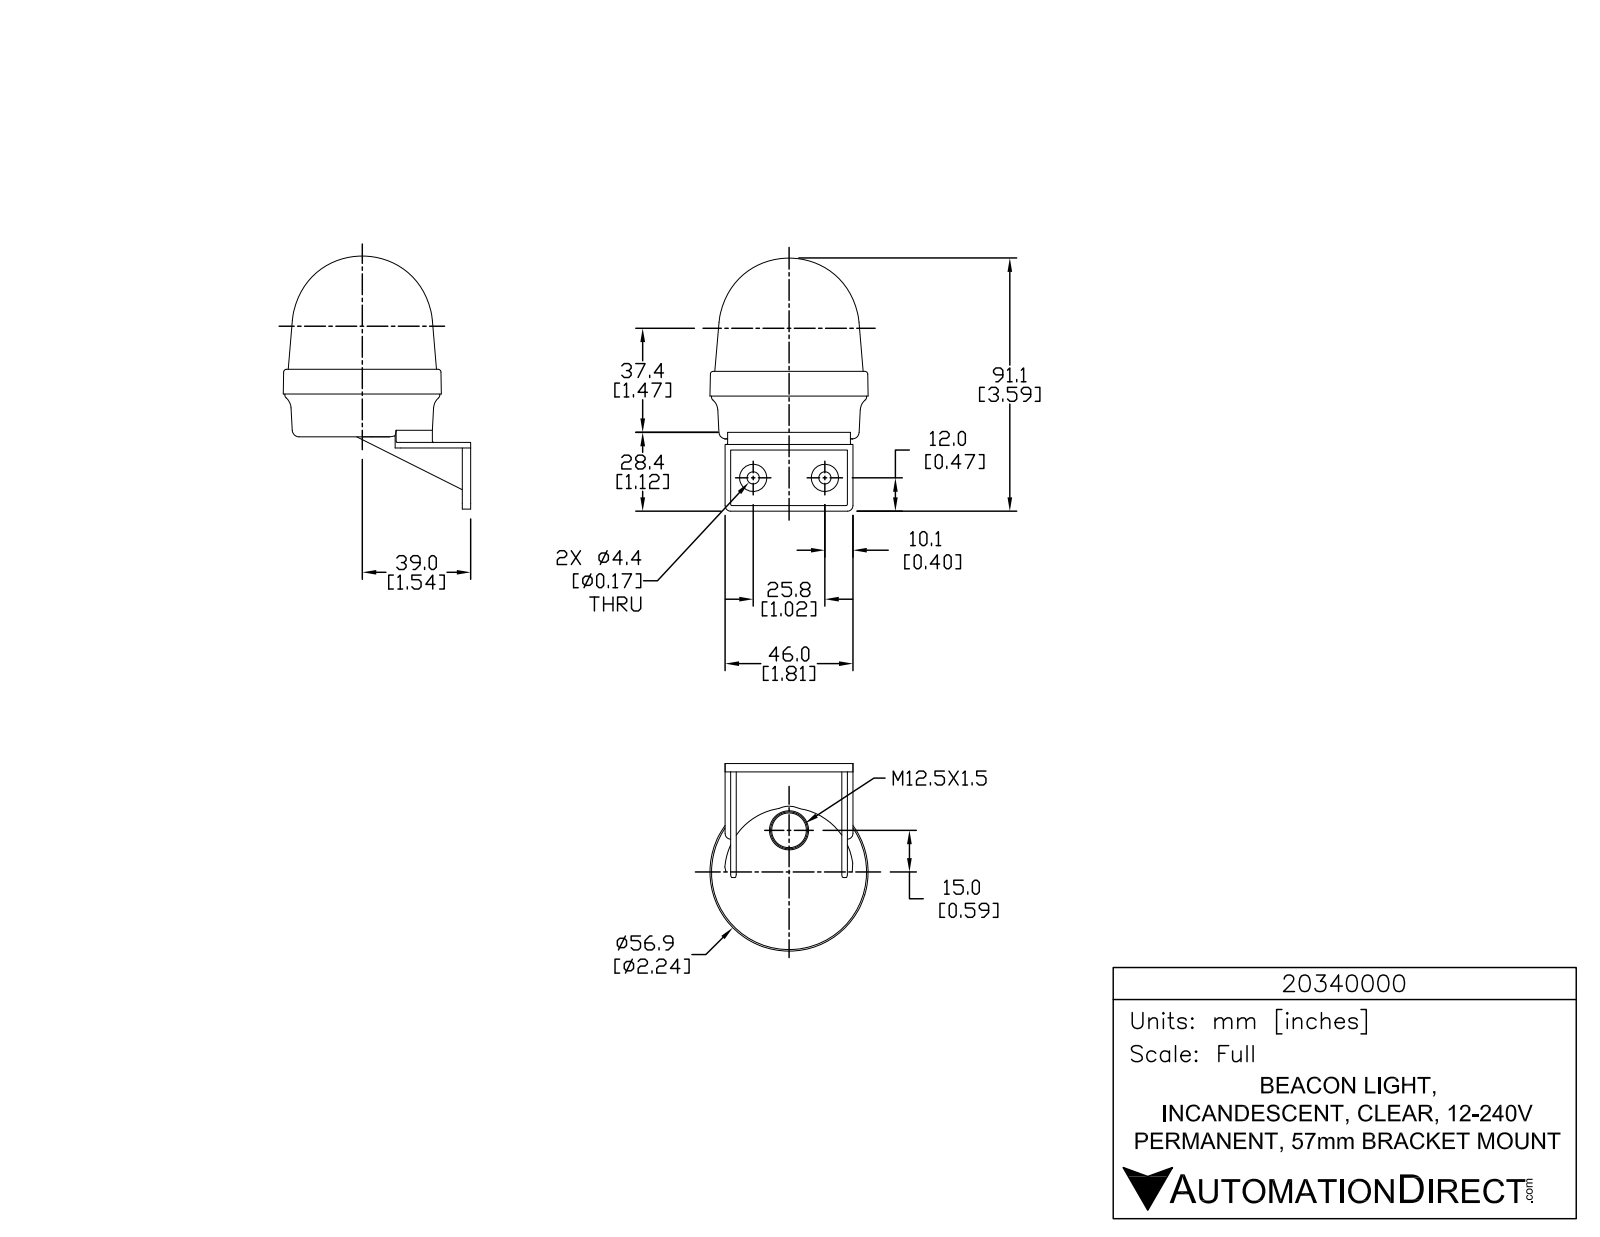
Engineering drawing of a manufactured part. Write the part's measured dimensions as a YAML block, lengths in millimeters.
part_name: "20340000"
step_written_by: "SolidWorks 2015 (AUTOMOTIVE_DESIGN)"
units: millimeters
bodies: {solids: 1, faces: 813, planar: 550, cylindrical: 169, other: 94}
overall_size: [91.1, 72.07, 60.76]
volume: 126840
surface_area: 18525
round_holes:
  - {diameter: 0.99, count: 3}
  - {diameter: 4.4, count: 2}
round_bosses_or_shafts:
  - {diameter: 5.74, count: 3}
  - {diameter: 1.43, count: 3}
  - {diameter: 9.8, count: 2}
  - {diameter: 55.8, count: 1}
partial_cylinders:
  - {radius: 0.2, count: 6}
  - {radius: 0.21, count: 6}
  - {radius: 0.21, count: 6}
  - {radius: 0.5, count: 6}
  - {radius: 3.32, count: 6}
  - {radius: 2, count: 4}
  - {radius: 0.1, count: 3}
  - {radius: 0.12, count: 3}
face_to_face_distances: [2, 4, 40, 42, 1, 3, 38, 22, 24, 44.01]
hole_center_spacings: [25.8]
